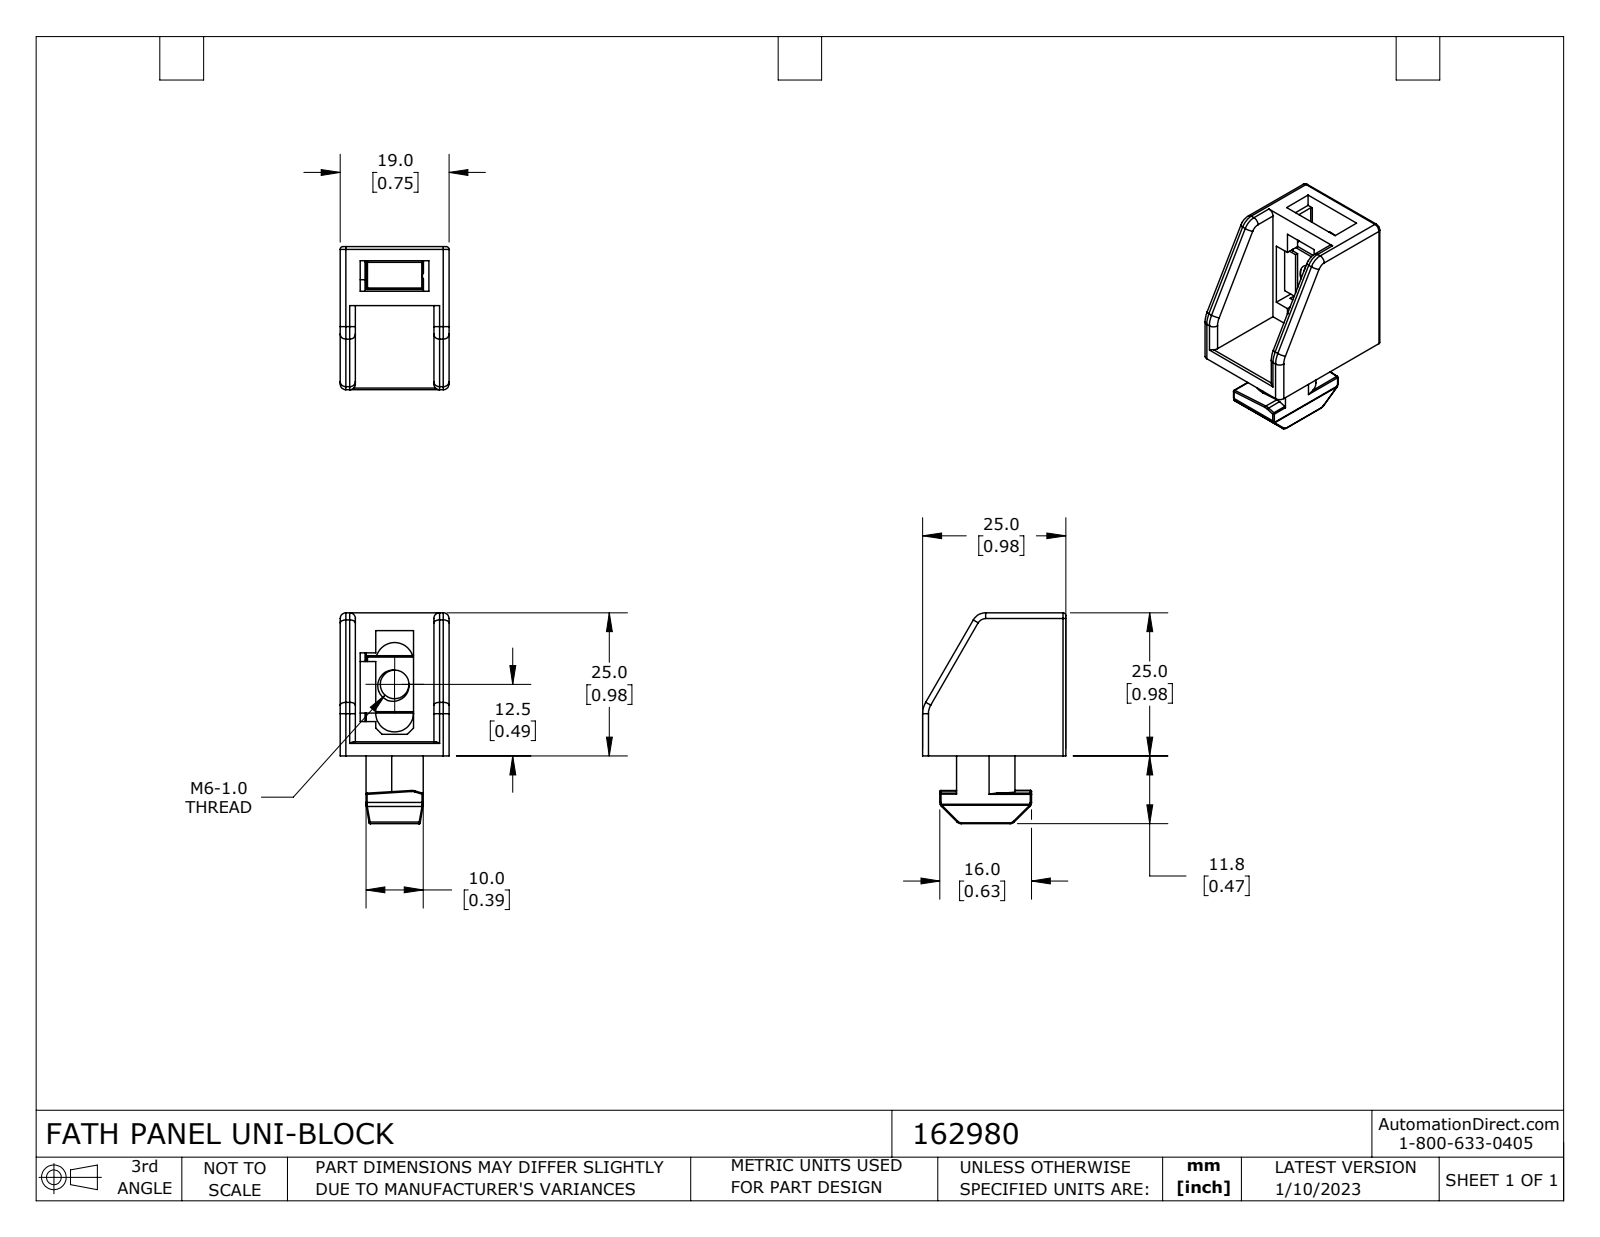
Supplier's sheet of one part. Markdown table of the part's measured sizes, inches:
| quantity | value |
| --- | --- |
| part name | 162980 |
| STEP written by | SolidWorks 2021 (CONFIG_CONTROL_DESIGN) |
| units | inches |
| bodies | 2 solids, 186 faces (63 planar, 80 cylindrical, 43 other) |
| overall size | 1.449 × 0.984 × 0.748 |
| volume | 0.411 in³ |
| surface area | 7.715 in² |
| round holes (diameter × count) | 0.079 × 2, 0.197 × 1 |
| partial cylindrical surfaces (radius × count) | 0.008 × 20, 0.039 × 18, 0.01 × 12, 0.02 × 3, 0.079 × 2, 0.13 × 2, 0.177 × 2, 0.012 × 1 |
| main face-to-face distances | 0.098, 0.748, 0.104, 0.644, 0.307, 0.073, 0.539, 0.571, 0.177, 0.467 |
| hole center spacings | 0.284, 0.472 |
